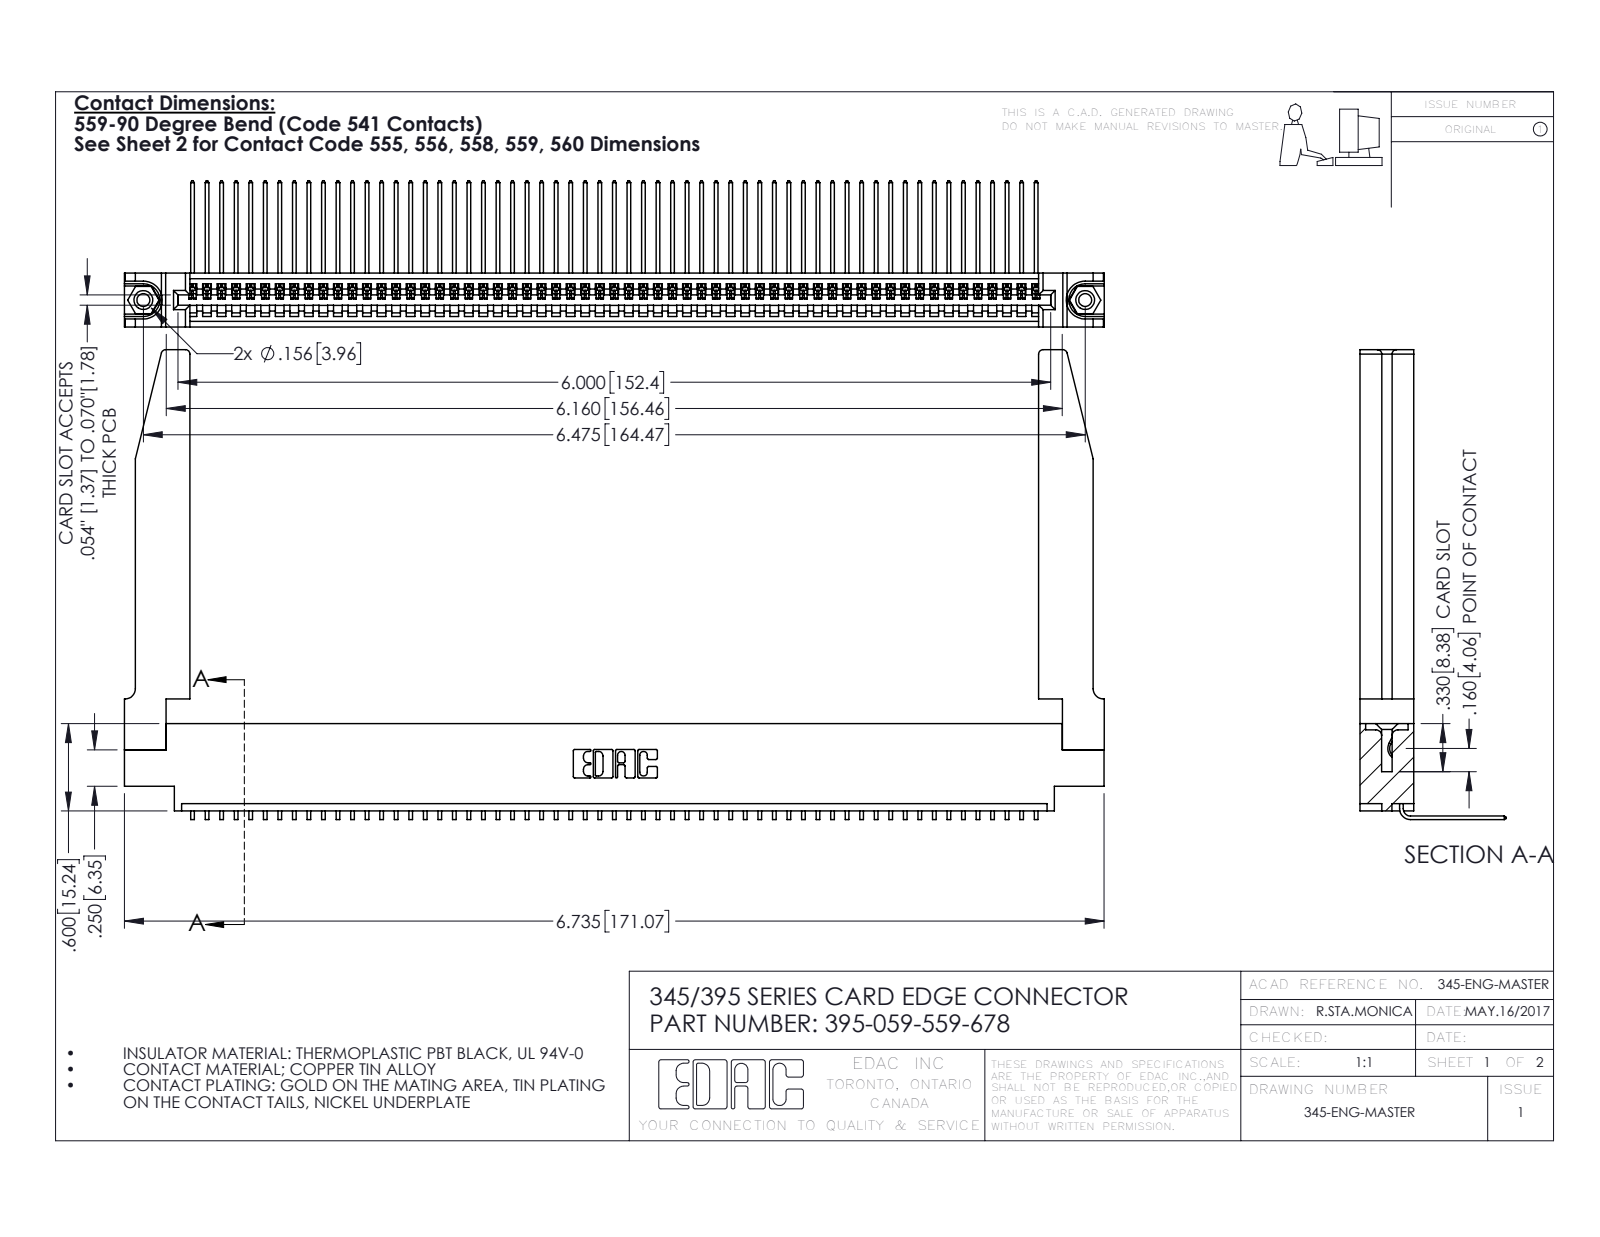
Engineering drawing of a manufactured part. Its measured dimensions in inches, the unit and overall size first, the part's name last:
Units: inches
Overall size (bounding box): 6.736 × 3.229 × 1.005
Round holes (diameter × count): ⌀0.089 ×2, ⌀0.125 ×2, ⌀0.156 ×2, ⌀0.064 ×1
Round bosses / shafts (diameter × count): ⌀0.155 ×2
Partial cylindrical surfaces — rounded edges, fillets, slot ends (radius × count): R0.006 ×118, R0.01 ×22, R0.03 ×8, R0.007 ×6, R0.031 ×6, R0.026 ×3, R0.031 ×2, R0.04 ×2
Main face-to-face distances: 0.37, 0.072, 0.298, 0.098, 0.272, 0.025, 0.2, 0.225, 0.148, 0.15
Hole centre spacings: 0.27, 6.239, 6.475
Volume: 1.479 in³ · Surface area: 46.89 in²
Bodies: 64 solids, 3904 faces (2704 planar, 1148 cylindrical, 52 other)
Part name (STEP PRODUCT): 345-250-001_345-250-001-102; 345-220-078_345-220-078; 345-292-001_558 559 Tail - 1; 345 Part_0.170 Offset - 0.156 Dia-TH (+1 more)
STEP written by: SolidWorks 2016 (CONFIG_CONTROL_DESIGN)
